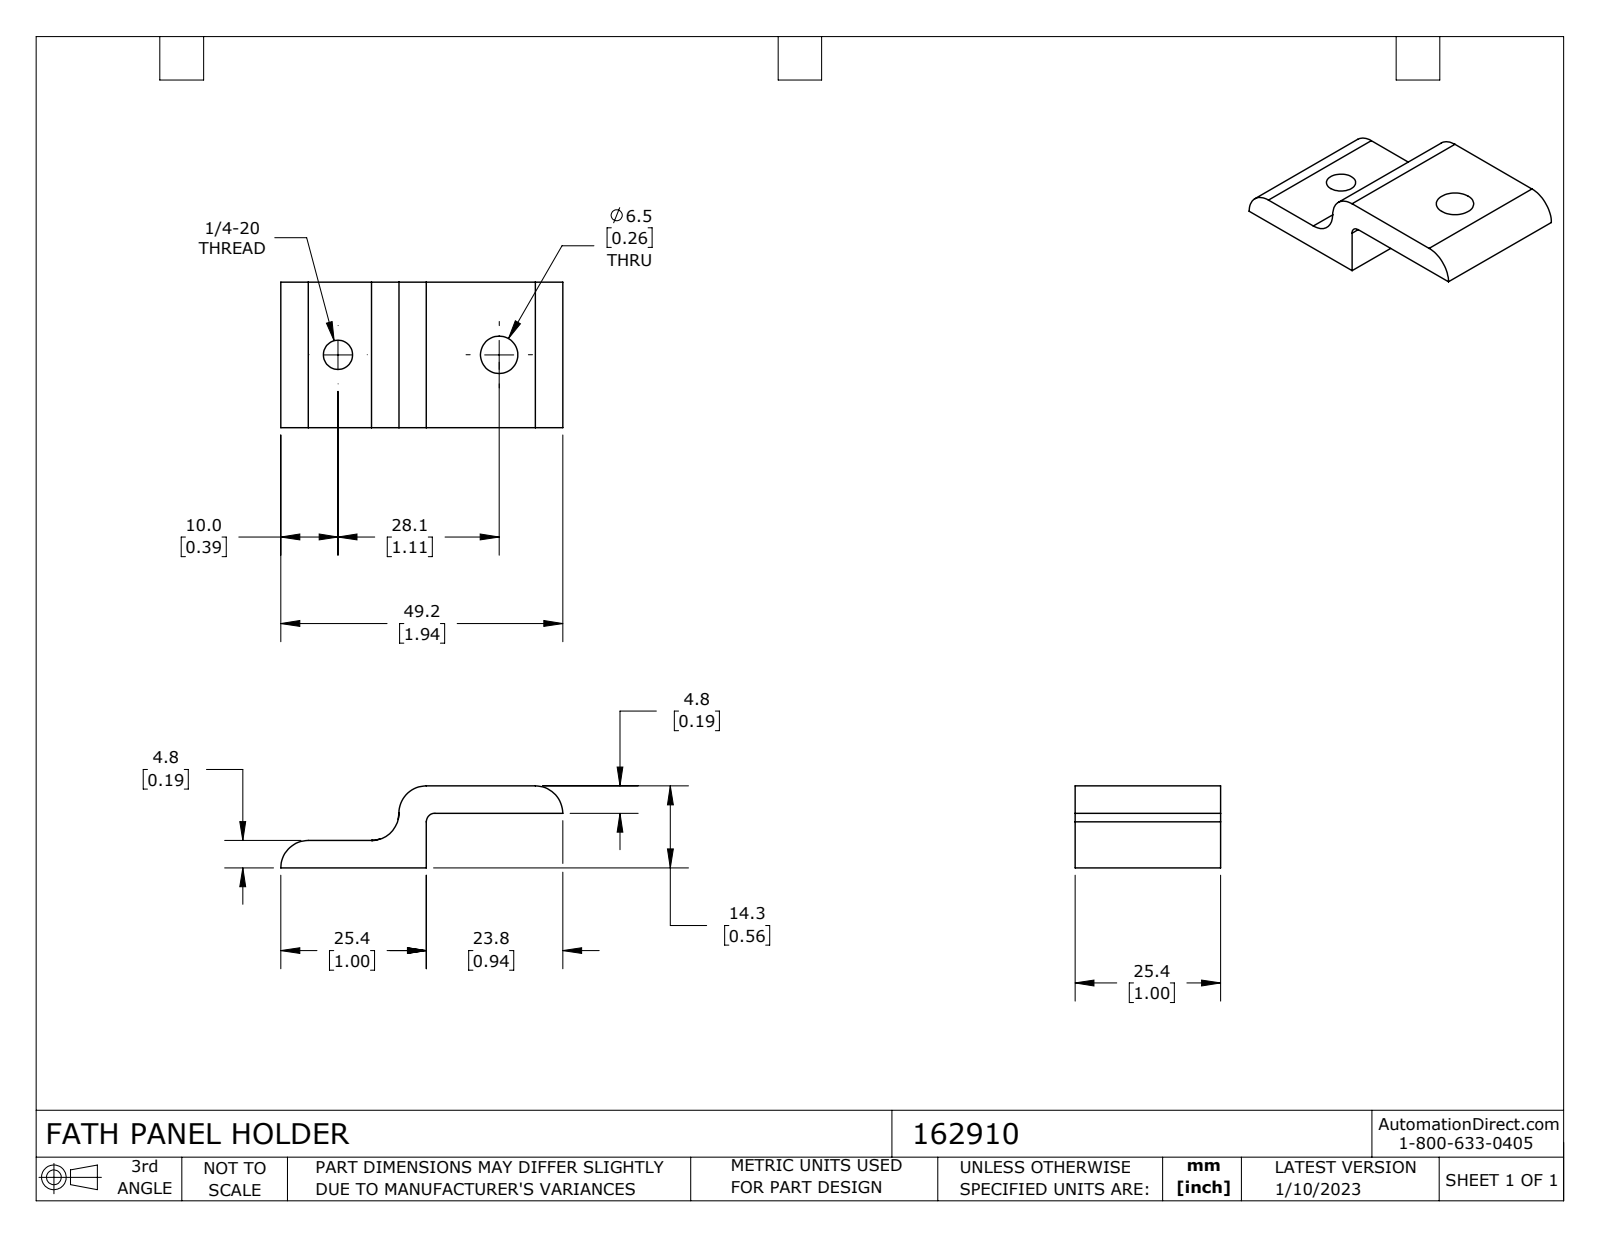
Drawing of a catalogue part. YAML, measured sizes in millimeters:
part_name: "162910"
step_written_by: "SolidWorks 2021 (CONFIG_CONTROL_DESIGN)"
units: millimeters
bodies: {solids: 1, faces: 16, planar: 7, cylindrical: 8, other: 1}
overall_size: [49.2, 25.4, 14.3]
volume: 6640
surface_area: 3614
round_holes:
  - {diameter: 5.1, count: 1}
  - {diameter: 6.5, count: 1}
partial_cylinders:
  - {radius: 4.8, count: 2}
  - {radius: 1.5, count: 1}
  - {radius: 4.8, count: 1}
face_to_face_distances: [9.5, 4.8, 14.3, 25.4, 4.7]
hole_center_spacings: [28.1]
